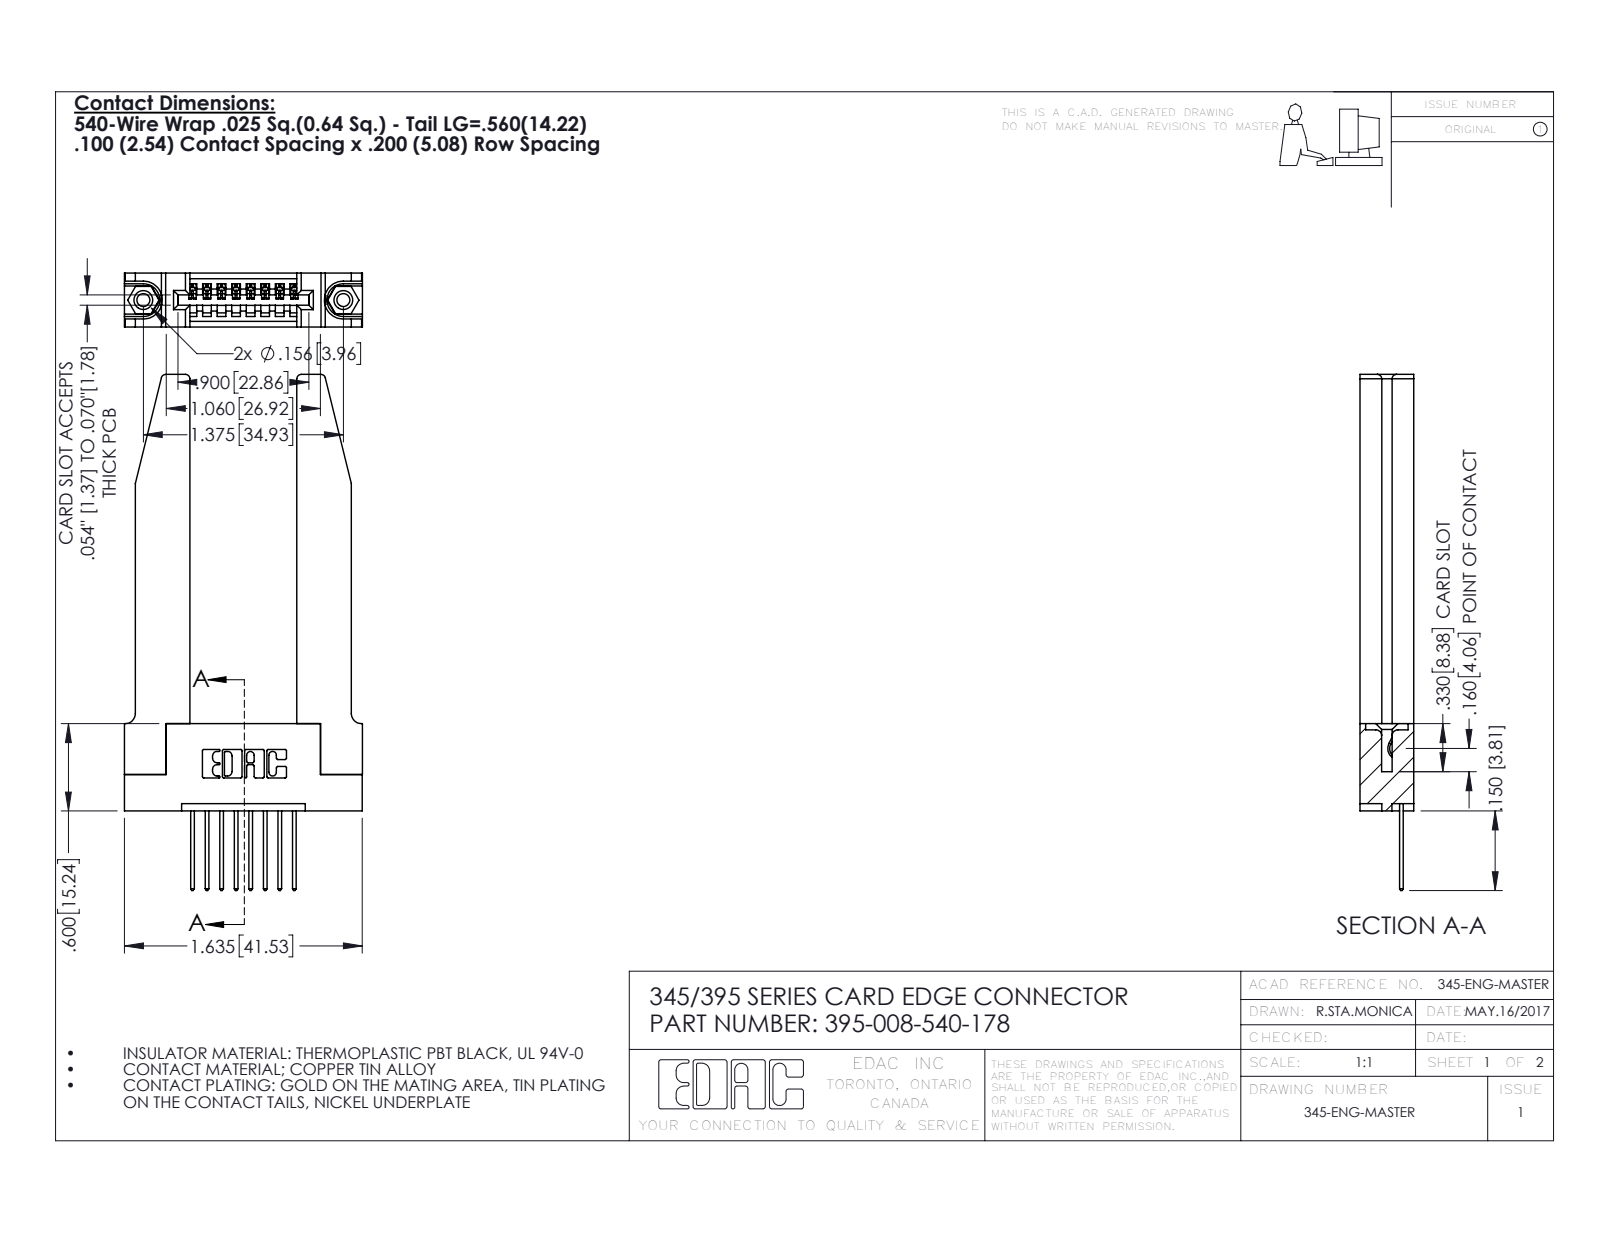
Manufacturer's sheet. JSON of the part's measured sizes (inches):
{"part_name": "345-220-078_345-220-078; 345-292-001_345-293-140; 395-008-540-178; 345 Part_Flush Mounting Lugs - 0.156 Dia-TH (+1 more)", "step_written_by": "SolidWorks 2016 (CONFIG_CONTROL_DESIGN)", "units": "inches", "bodies": {"solids": 13, "faces": 824, "planar": 542, "cylindrical": 230, "other": 52}, "overall_size": [3.547, 1.636, 0.37], "volume_in3": 0.699, "surface_area_in2": 17.59, "round_holes": [[0.089, 2], [0.125, 2], [0.156, 2], [0.064, 1]], "round_bosses_or_shafts": [[0.155, 2]], "partial_cylinders_radius": [[0.01, 22], [0.006, 16], [0.01, 16], [0.03, 8], [0.007, 6], [0.031, 6], [0.026, 3], [0.031, 2]], "face_to_face_distances": [0.37, 0.072, 0.15, 0.298, 0.22, 0.148, 0.735, 0.077, 0.2, 0.098], "hole_center_spacings": [0.27, 1.144, 1.375]}
